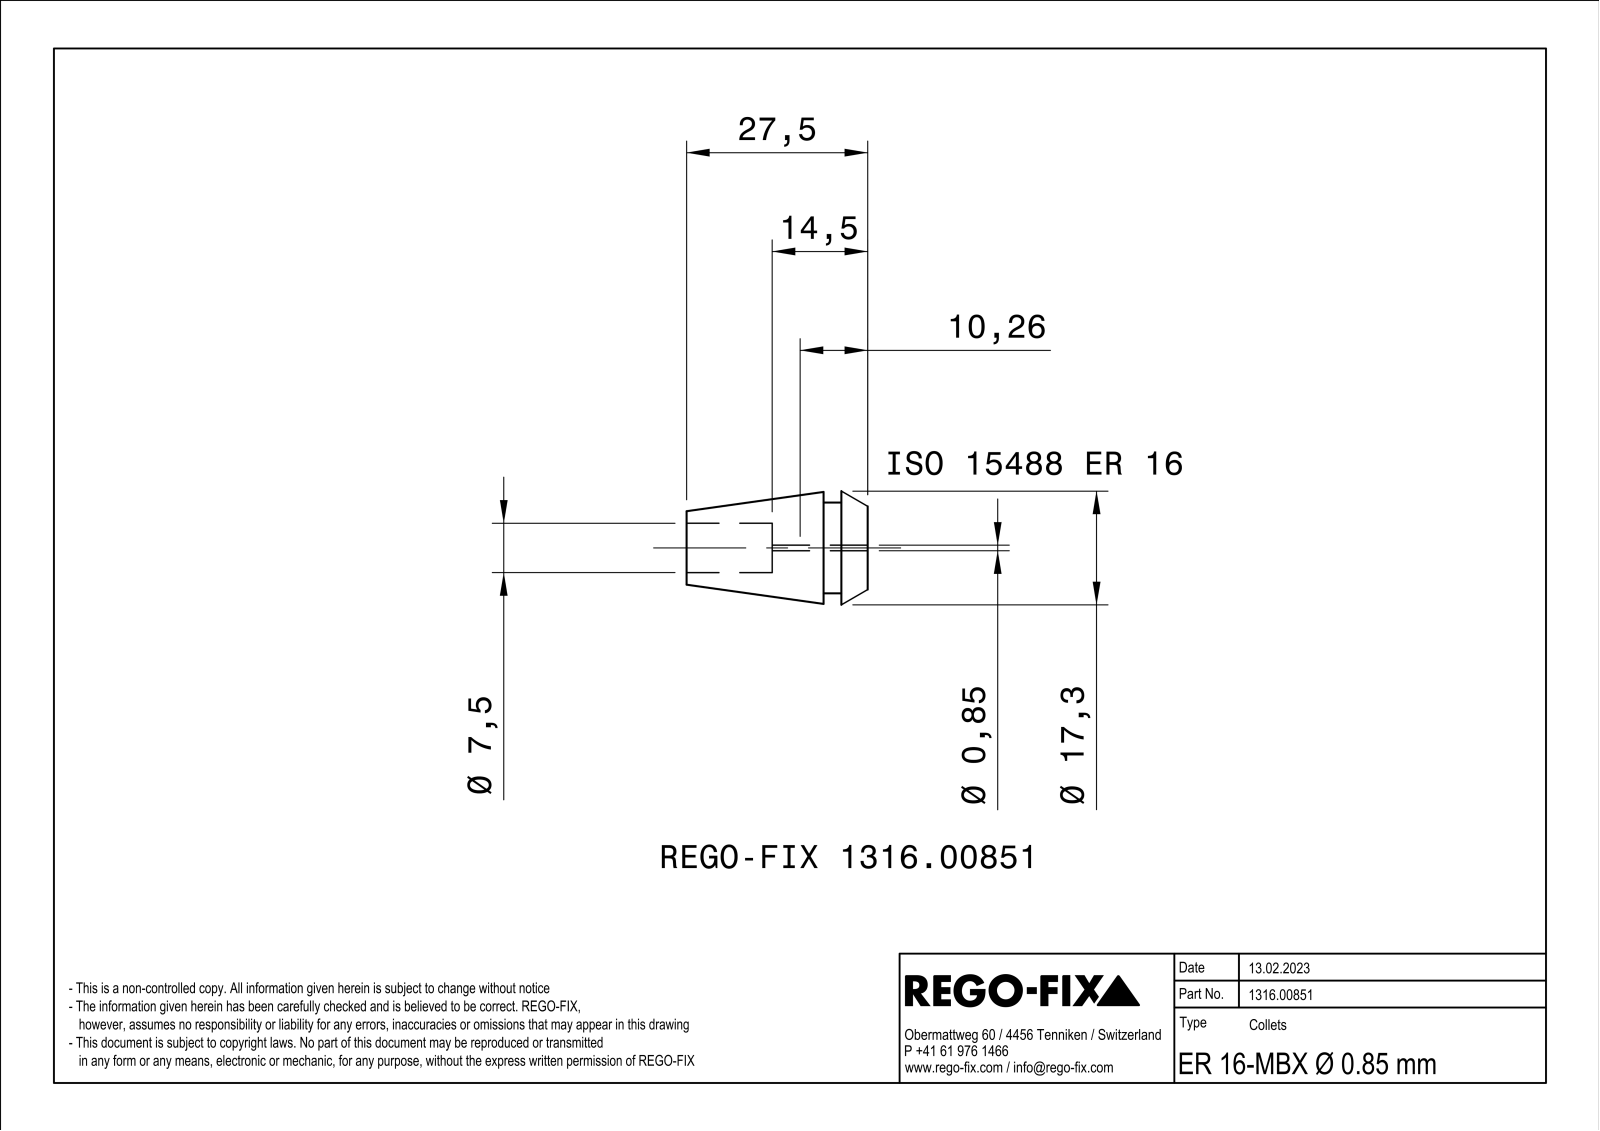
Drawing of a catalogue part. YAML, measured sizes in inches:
part_name: "NOCUT"
step_written_by: "SIEMENS PLM Software Solid Edge ST10 (AUTOMOTIVE_DESIGN)"
units: inches
bodies: {solids: 1, faces: 109, planar: 36, cylindrical: 27, other: 46}
overall_size: [1.083, 0.666, 0.665]
volume: 0.201
surface_area: 5.143
round_holes:
  - {diameter: 0.079, count: 3}
  - {diameter: 0.295, count: 1}
round_bosses_or_shafts:
  - {diameter: 0.543, count: 1}
partial_cylinders:
  - {radius: 0.006, count: 3}
  - {radius: 0.984, count: 3}
  - {radius: 0.017, count: 1}
face_to_face_distances: [0.021, 0.031, 0.264, 0.157, 0.106, 1.083, 0.925, 0.819, 0.571, 0.413]
hole_center_spacings: [0.083, 0.143]
